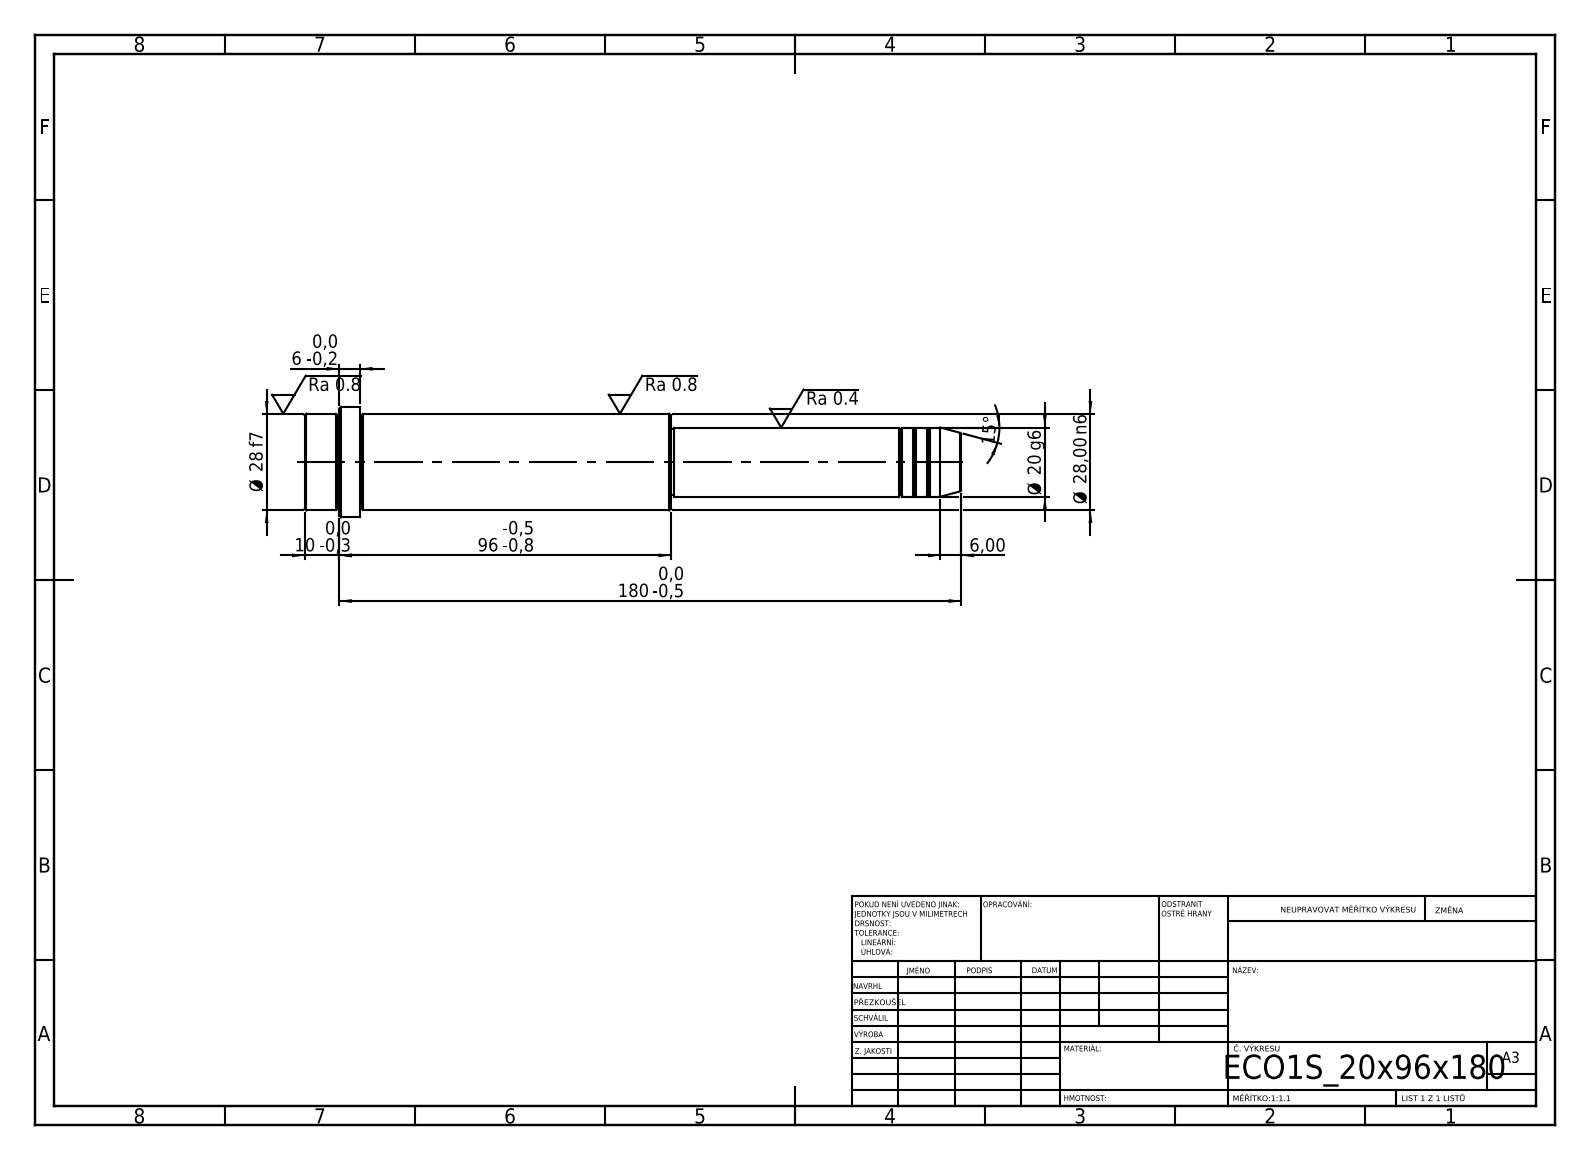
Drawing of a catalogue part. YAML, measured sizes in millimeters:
step_written_by: "SolidWorks 2019 (CONFIG_CONTROL_DESIGN)"
units: millimeters
bodies: {solids: 1, faces: 52, planar: 6, cylindrical: 16, other: 30}
overall_size: [190, 32, 32]
volume: 92297
surface_area: 16338
round_bosses_or_shafts:
  - {diameter: 32, count: 1}
  - {diameter: 28, count: 1}
  - {diameter: 20, count: 1}
  - {diameter: 19, count: 1}
face_to_face_distances: [106, 84, 190, 174, 90, 16, 180, 96, 6, 10]
